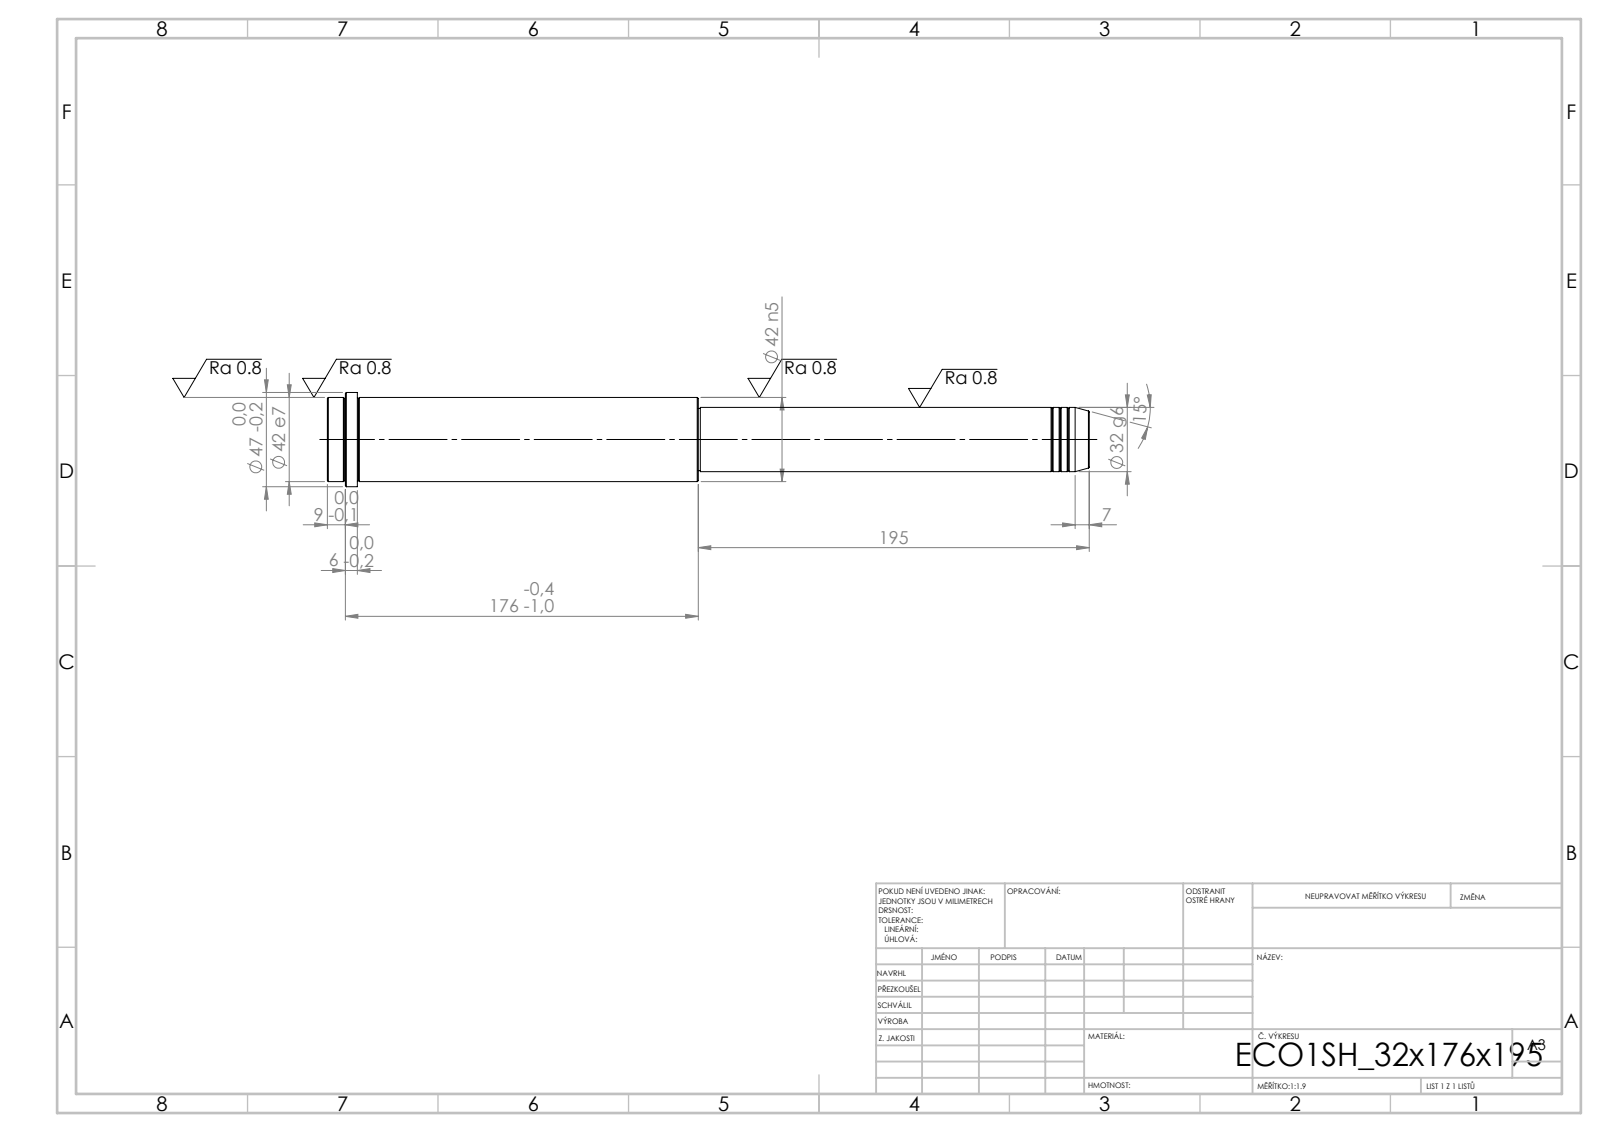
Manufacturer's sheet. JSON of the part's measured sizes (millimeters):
{"step_written_by": "SolidWorks 2019 (CONFIG_CONTROL_DESIGN)", "units": "millimeters", "bodies": {"solids": 1, "faces": 52, "planar": 6, "cylindrical": 16, "other": 30}, "overall_size": [380, 47, 47], "volume_mm3": 414276, "surface_area_mm2": 47654, "round_bosses_or_shafts": [[47, 1], [42, 1], [32, 1], [31, 1]], "face_to_face_distances": [380, 195, 185, 365, 170, 15, 371, 176, 6, 9]}
